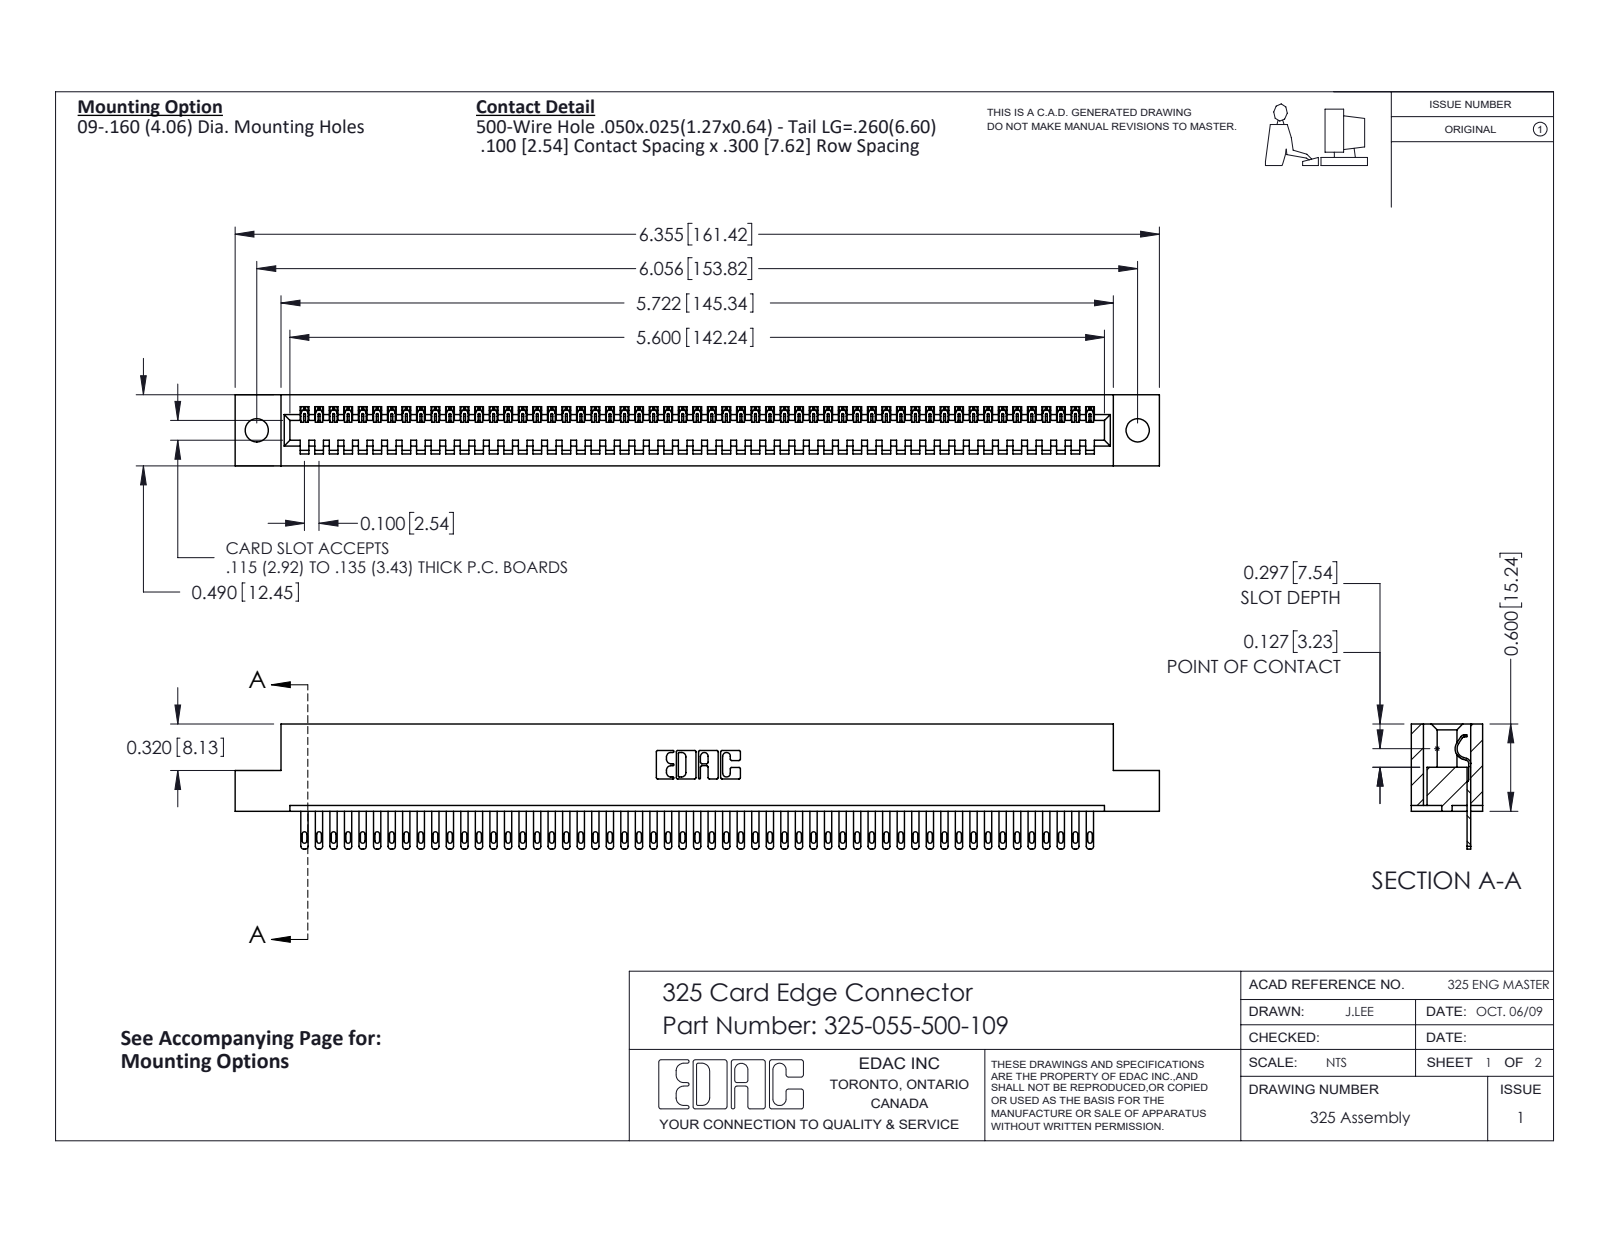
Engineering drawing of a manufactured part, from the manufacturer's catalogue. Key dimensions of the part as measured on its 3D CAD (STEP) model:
Part name (STEP PRODUCT): 325-292-001_325-293-100; 325 Part_.160 TH; 325-055-500-109
STEP written by: SolidWorks 2016 (CONFIG_CONTROL_DESIGN)
Units: inches
Bodies: 56 solids, 3084 faces (2050 planar, 1034 cylindrical, 0 other)
Overall size (bounding box): 6.355 × 0.86 × 0.49
Volume: 1.245 in³ · Surface area: 34.92 in²
Round holes (diameter × count): ⌀0.16 ×2
Partial cylindrical surfaces — rounded edges, fillets, slot ends (radius × count): R0.006 ×110, R0.016 ×110, R0.02 ×110, R0.01 ×22, R0.007 ×6, R0.031 ×6, R0.026 ×3, R0.014 ×1
Main face-to-face distances: 0.083, 0.407, 0.49, 0.3, 0.107, 0.383, 0.025, 0.325, 0.263, 0.56
Hole centre spacings: 6.056
